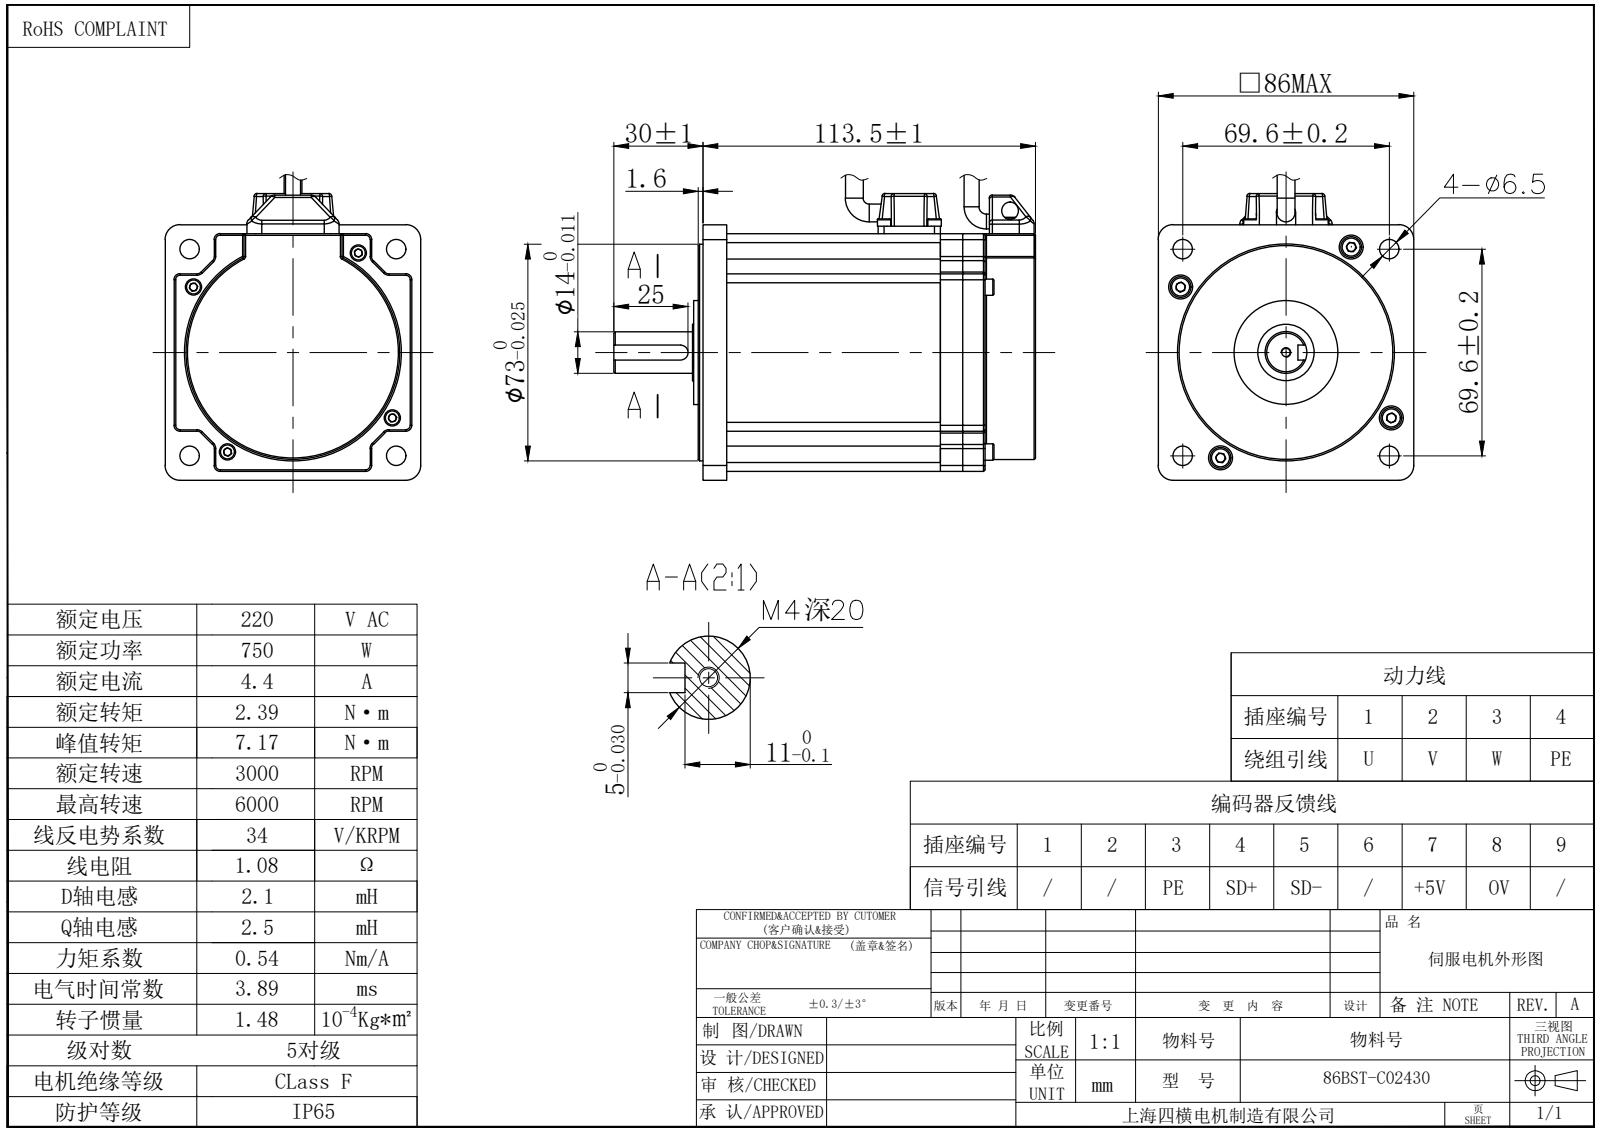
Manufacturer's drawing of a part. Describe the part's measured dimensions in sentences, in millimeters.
The part is named "hexagon socket head cap screws gb222_GB_FASTENER_SCREWS_HSHCS M2.5X16-N; 出轴; hexagon socket head cap screws gb222_GB_FASTENER_SCREWS_HSHCS M4X16-N; 43782_03 (+8 more)". Its 3-D file was written by "SolidWorks 2020 (AUTOMOTIVE_DESIGN)". It is 53 solids with 1705 faces: 773 planar, 668 cylindrical and 264 other. Overall it measures 179.11 by 143 by 86 millimeters. Its volume is 658 160 cubic millimeters and its surface area 111 419 square millimeters. Round holes: 9 of diameter 1, 9 of diameter 1.5, 6 of diameter 2.5, 6 of diameter 3, 4 of diameter 1.6, 4 of diameter 4.5, 4 of diameter 6.5, 4 of diameter 8, 2 of diameter 2.9, 2 of diameter 3.5, 2 of diameter 3.8, 2 of diameter 5.6. Round bosses or shafts: 9 of diameter 0.6, 8 of diameter 4.5, 6 of diameter 2.5, 5 of diameter 1.5, 4 of diameter 7, 4 of diameter 5.5, 4 of diameter 4, 4 of diameter 3. Partial cylindrical surfaces (rounded edges, fillets, slot ends): 55 of radius 1, 52 of radius 0.45, 38 of radius 2, 27 of radius 0.5, 12 of radius 3, 10 of radius 5, 9 of radius 0.97, 8 of radius 1.5. The main face-to-face distances are 80, 8, 72, 13.5, 33, 25, 105, 88, 66.5, 81.6. The hole center spacings are 3.16, 2.77, 5.54, 4, 12.82, 12.87, 17.73, 40.08.
